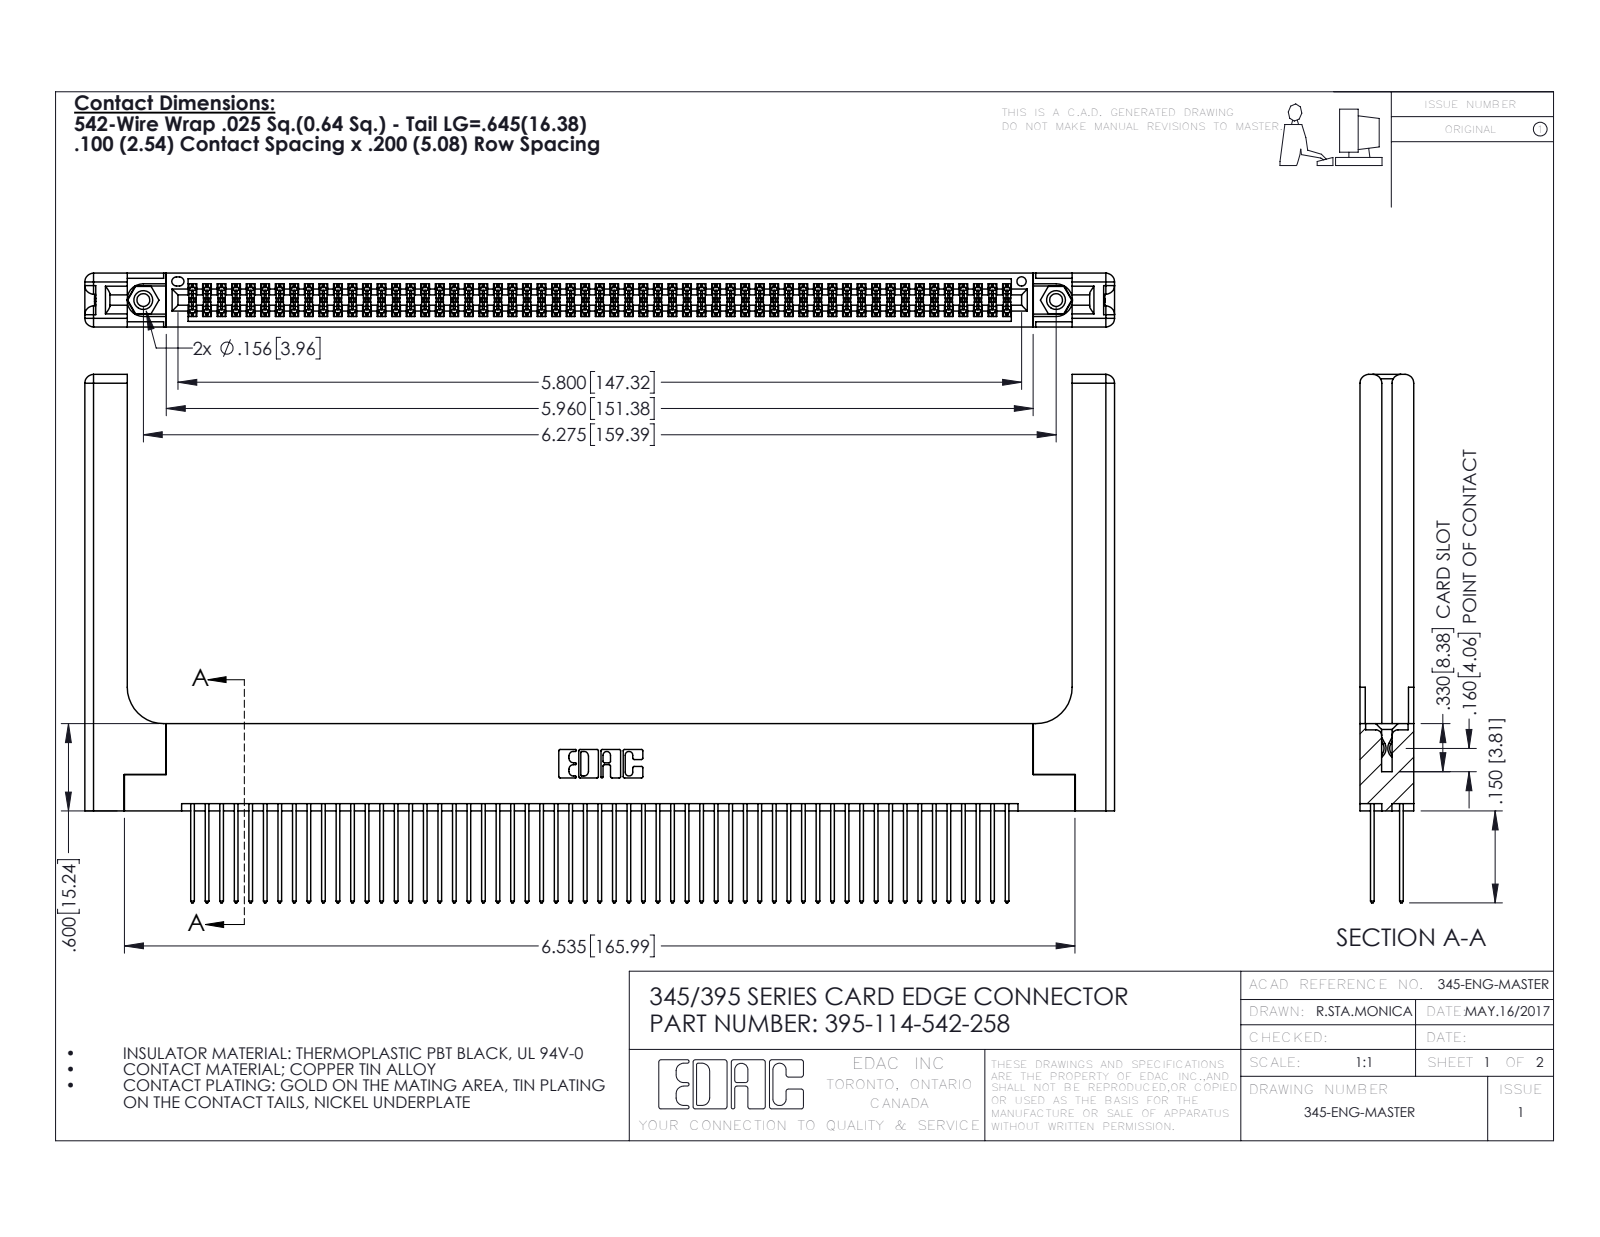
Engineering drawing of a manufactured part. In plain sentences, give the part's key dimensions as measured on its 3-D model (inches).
The part is named "345-292-001_345-293-142; 345-220-058_345-220-058; 395-114-542-258; 345-250-001_345-250-001-102 (+1 more)". Its 3-D file was written by "SolidWorks 2016 (CONFIG_CONTROL_DESIGN)". It is 119 solids with 6082 faces: 3990 planar, 2032 cylindrical and 60 other. Overall it measures 7.079 by 3.632 by 0.37 inches. Its volume is 1.624 cubic inches and its surface area 53.7 square inches. Round holes: 2 of diameter 0.089, 2 of diameter 0.125, 2 of diameter 0.156, 1 of diameter 0.064. Round bosses or shafts: 2 of diameter 0.155. Partial cylindrical surfaces (rounded edges, fillets, slot ends): 171 of radius 0.006, 114 of radius 0.01, 22 of radius 0.01, 16 of radius 0.06, 6 of radius 0.007, 6 of radius 0.031, 3 of radius 0.026, 2 of radius 0.014. The main face-to-face distances are 0.072, 0.298, 0.2, 0.37, 0.098, 0.272, 0.025, 0.225, 0.175, 0.148. The hole center spacings are 0.27, 6.039, 6.275.
